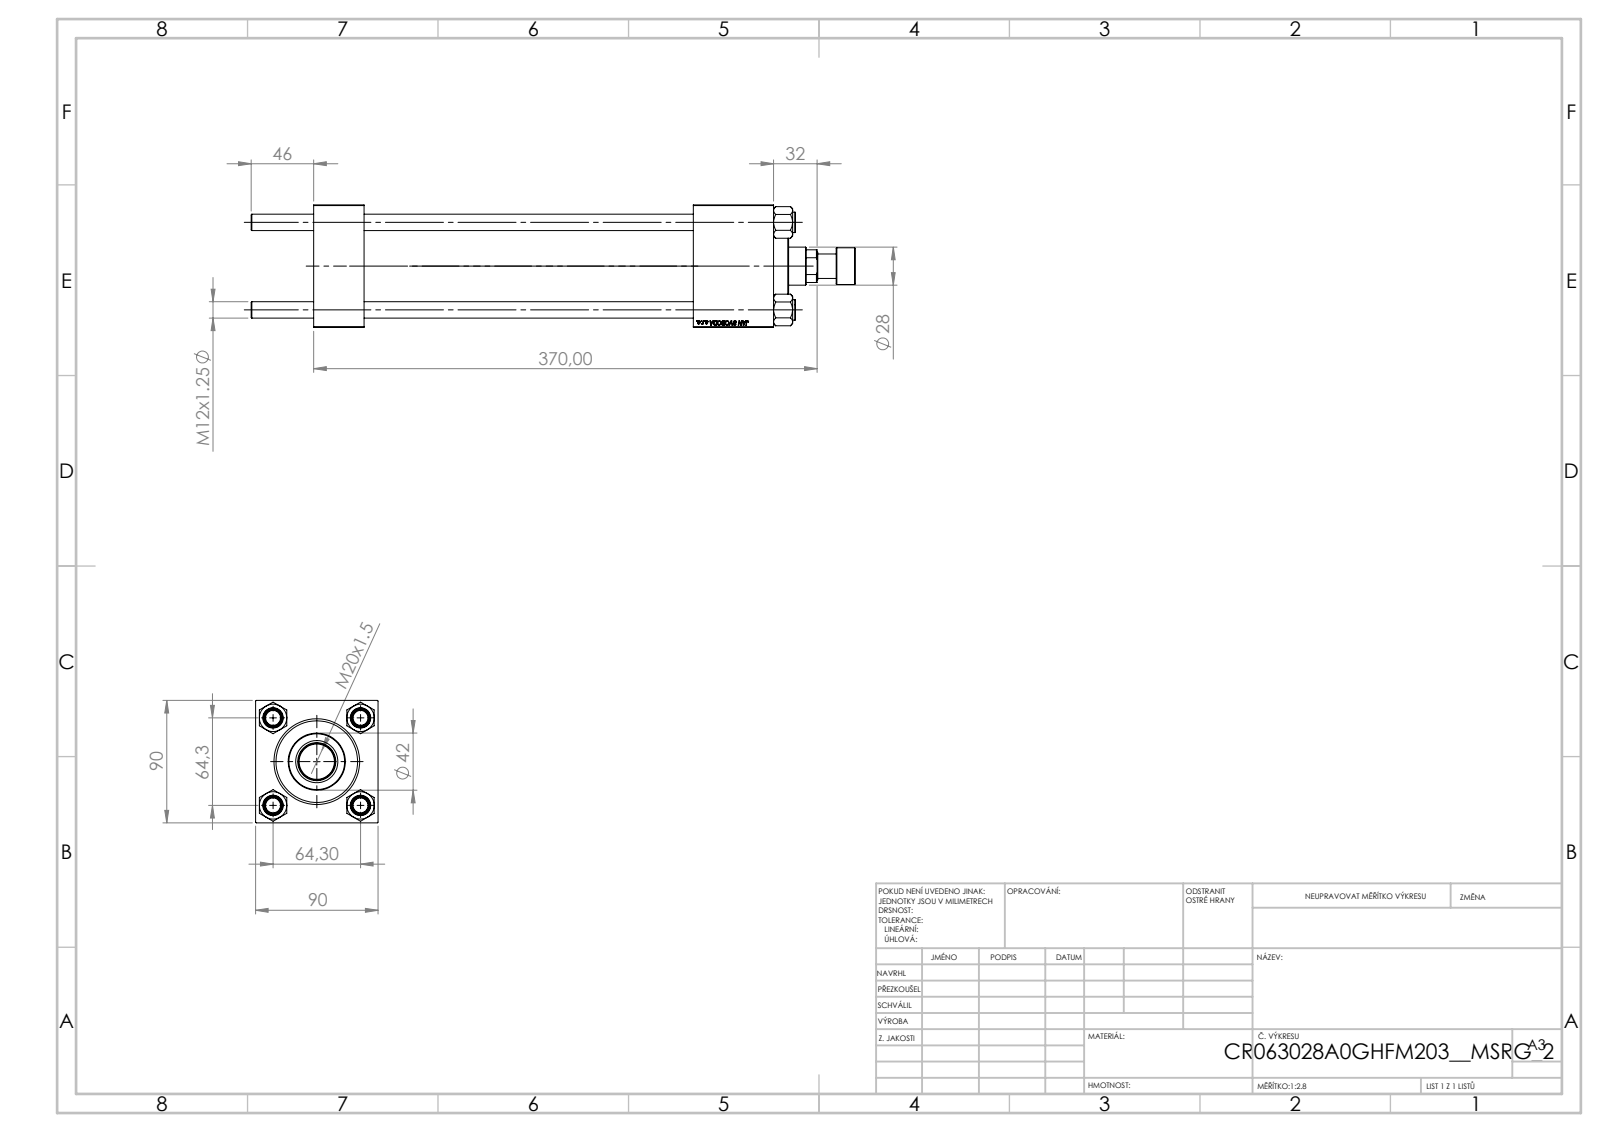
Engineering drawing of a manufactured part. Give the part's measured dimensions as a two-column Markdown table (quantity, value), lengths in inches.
| quantity | value |
| --- | --- |
| part name | V215CR_ROD_END_F; V215_VC_A; CR025_012_A_0_G_A_G_M_020_+#_##_TYCINKA; V215CR_BODY_A (+2 more) |
| STEP written by | SolidWorks 2019 (CONFIG_CONTROL_DESIGN) |
| units | inches |
| bodies | 12 solids, 1148 faces (524 planar, 82 cylindrical, 542 other) |
| overall size | 17.48 × 3.543 × 3.543 |
| volume | 79.45 in³ |
| surface area | 493.1 in² |
| round holes (diameter × count) | 0.472 × 4, 0.276 × 2, 0.825 × 2, 1.181 × 2, 0.728 × 1, 1.102 × 1, 1.22 × 1, 1.969 × 1, 2.362 × 1, 2.48 × 1 |
| round bosses / shafts (diameter × count) | 0.591 × 4, 2.717 × 1, 1.654 × 1, 1.063 × 1, 0.709 × 1 |
| main face-to-face distances | 3.543, 1.457, 13.307, 11.85, 10.984, 9.528, 2.323, 12.177, 10.72, 1.193 |
| hole center spacings | 1.79, 2.531, 3.58, 11.043 |
